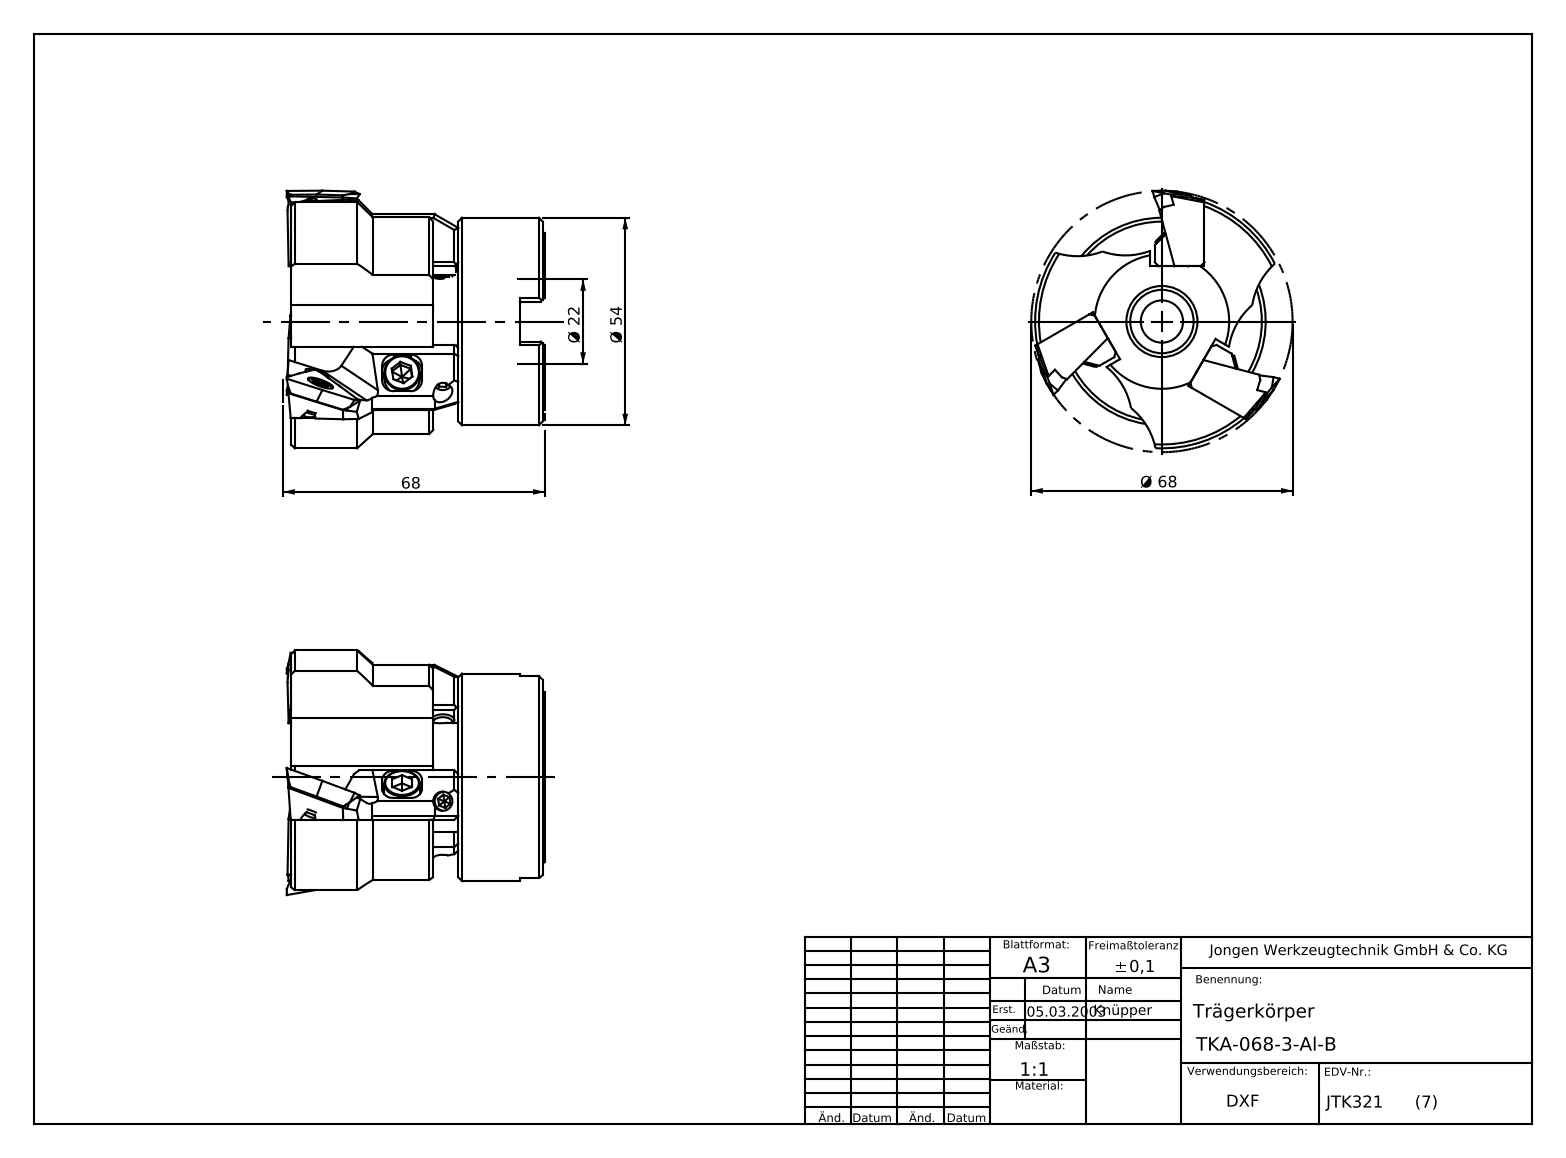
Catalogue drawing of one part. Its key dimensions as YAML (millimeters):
part_name: "TKA-068-3-Al-B"
step_written_by: "SolidWorks 2012 (AUTOMOTIVE_DESIGN)"
units: millimeters
bodies: {solids: 1, faces: 158, planar: 56, cylindrical: 62, other: 40}
overall_size: [68, 68, 68]
volume: 134318
surface_area: 27349
round_holes:
  - {diameter: 5, count: 6}
  - {diameter: 6, count: 3}
  - {diameter: 11, count: 1}
  - {diameter: 16.5, count: 1}
  - {diameter: 22, count: 1}
  - {diameter: 22.05, count: 1}
  - {diameter: 22.3, count: 1}
  - {diameter: 24.76, count: 1}
round_bosses_or_shafts:
  - {diameter: 68, count: 1}
  - {diameter: 54, count: 1}
  - {diameter: 46, count: 1}
  - {diameter: 28.5, count: 1}
partial_cylinders:
  - {radius: 3, count: 12}
  - {radius: 18, count: 6}
  - {radius: 29.25, count: 1}
  - {radius: 33, count: 1}
face_to_face_distances: [16.9, 27.9, 44.8, 22.5, 50.4, 67.3, 29, 6.5, 21.4, 38.3]
